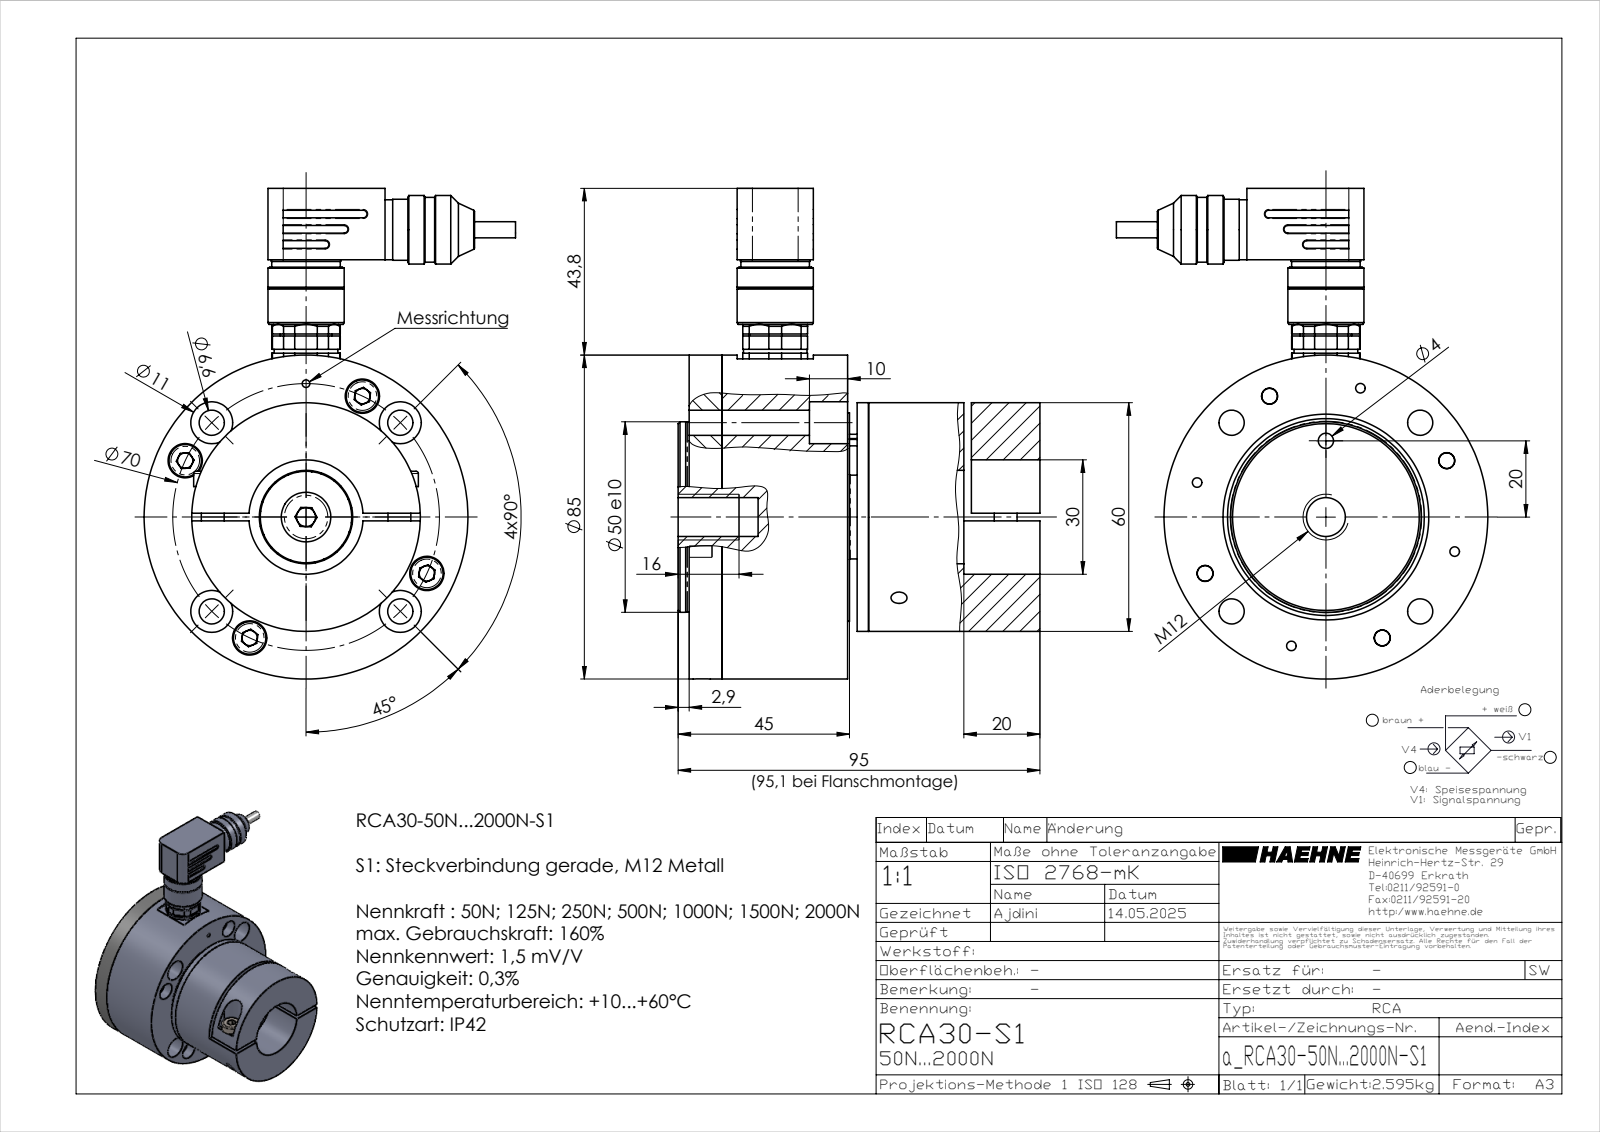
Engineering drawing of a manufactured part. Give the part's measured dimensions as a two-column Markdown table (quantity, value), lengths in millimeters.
| quantity | value |
| --- | --- |
| part name | Washer DIN 9021 - 8.4_Washer DIN 9021 - 8.4; inafag_1203-tvh_7zkvytp7yxkimpdvw8sj0b5w4_20; inafag_1203-tvh_7zkvytp7yxkimpdvw8sj0b5w4_05; DIN 7984 - M8 x 12 --- 8.25N_DIN 7984 - M8 x 12 --- 8.25N (+8 more) |
| STEP written by | SolidWorks 2023 (AUTOMOTIVE_DESIGN) |
| units | millimeters |
| bodies | 55 solids, 808 faces (408 planar, 228 cylindrical, 172 other) |
| overall size | 128.75 × 97.48 × 95.1 |
| volume | 376 857 mm³ |
| surface area | 116 381 mm² |
| round holes (diameter × count) | 3.4 × 9, 2.5 × 8, 6.6 × 6, 4.2 × 5, 4 × 4, 5.3 × 4, 9 × 4, 11 × 4, 4.5 × 2, 5 × 2, 2 × 1, 6 × 1 |
| round bosses / shafts (diameter × count) | 3 × 9, 5.7 × 8, 8.5 × 4, 5 × 4, 1.5 × 4, 1 × 4, 18 × 2, 17 × 2 |
| partial cylindrical surfaces (radius × count) | 0.2 × 12, 1 × 11, 0.3 × 6, 4 × 2, 5.5 × 2, 0.57 × 1, 0.65 × 1, 0.77 × 1 |
| main face-to-face distances | 2, 3, 8.6, 47.1, 35.5, 11.6, 45, 50, 30, 50.1 |
| hole center spacings | 35, 49.5, 24.78, 25.2, 32.8, 51.14, 56.46, 6 |
